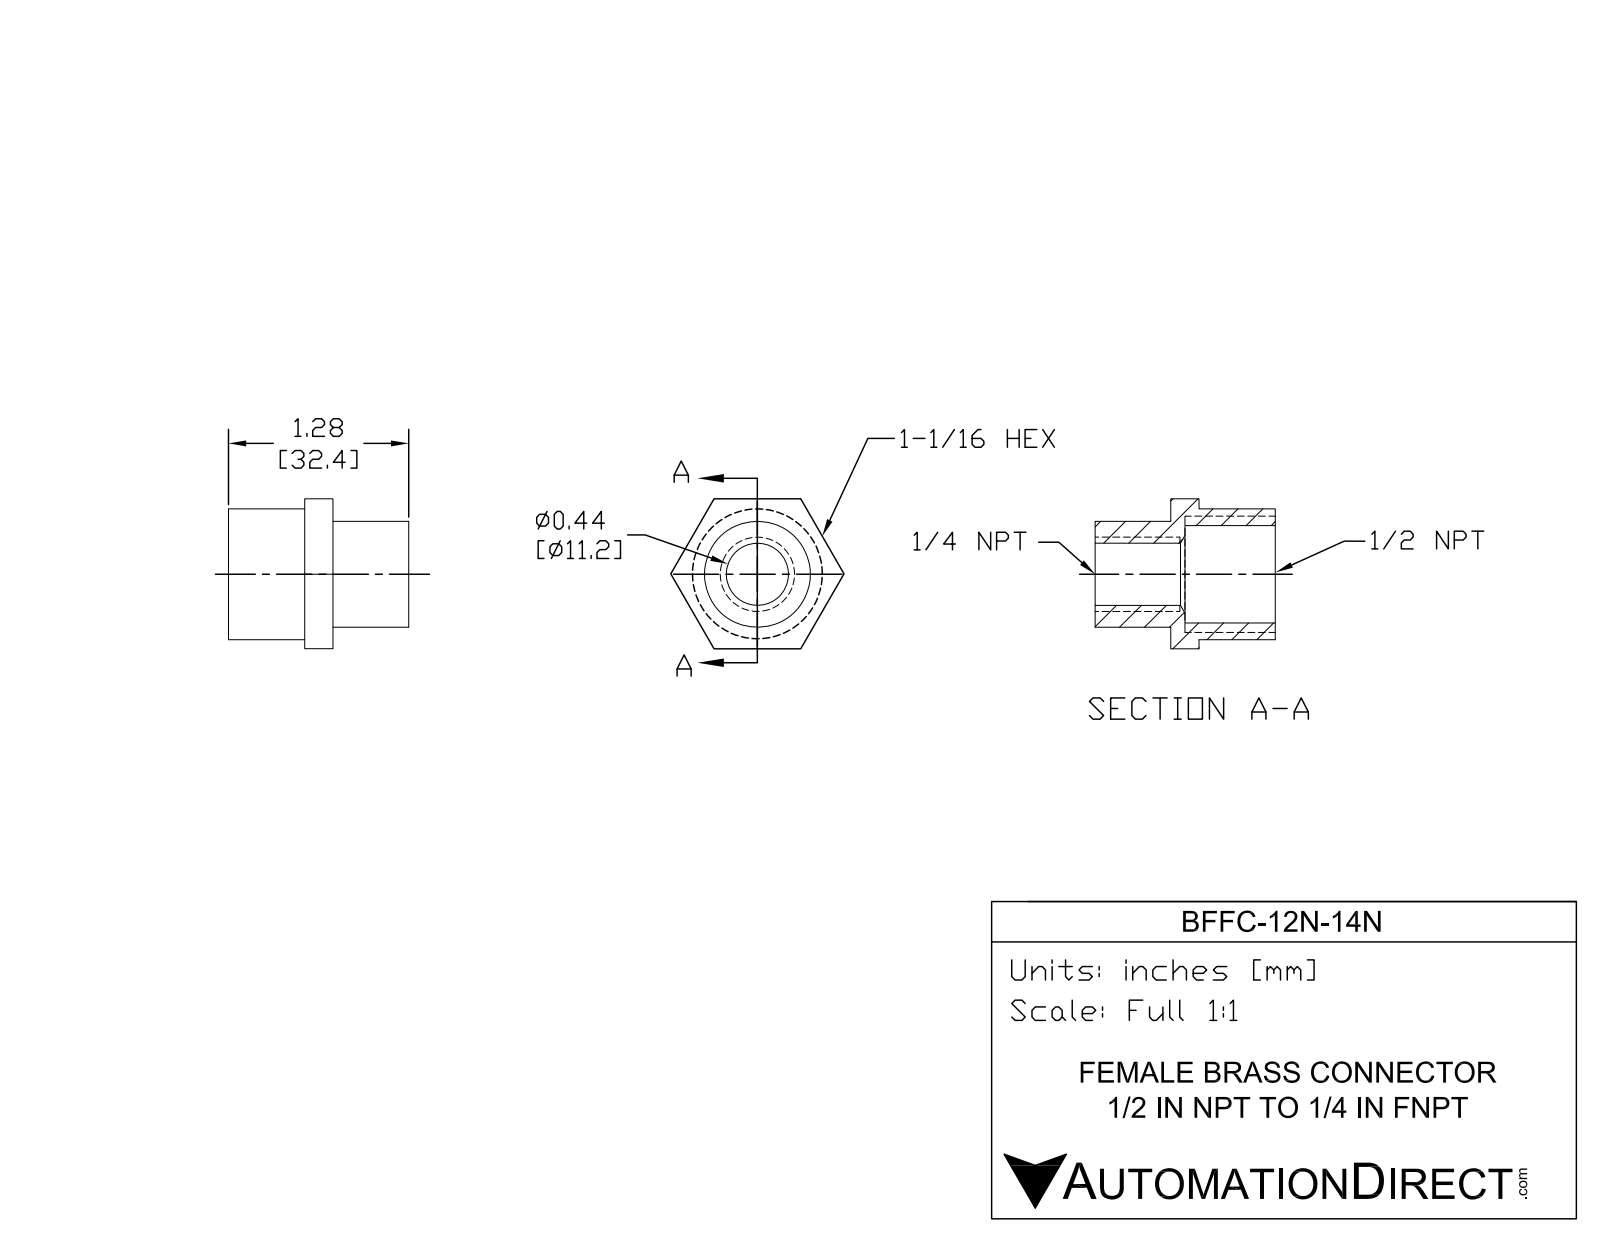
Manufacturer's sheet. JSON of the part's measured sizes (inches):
{"part_name": "BFFC-12N-14N", "step_written_by": "SolidWorks 2015 (CONFIG_CONTROL_DESIGN)", "units": "inches", "bodies": {"solids": 1, "faces": 21, "planar": 11, "cylindrical": 8, "other": 2}, "overall_size": [1.276, 1.227, 1.062], "volume_in3": 0.459, "surface_area_in2": 7.457, "round_holes": [[0.44, 1], [0.69, 1]], "round_bosses_or_shafts": [[0.926, 1], [0.75, 1]], "face_to_face_distances": [1.062, 0.2, 0.74, 0.54, 0.536, 0.736, 1.276, 0.1, 0.636, 0.64]}
